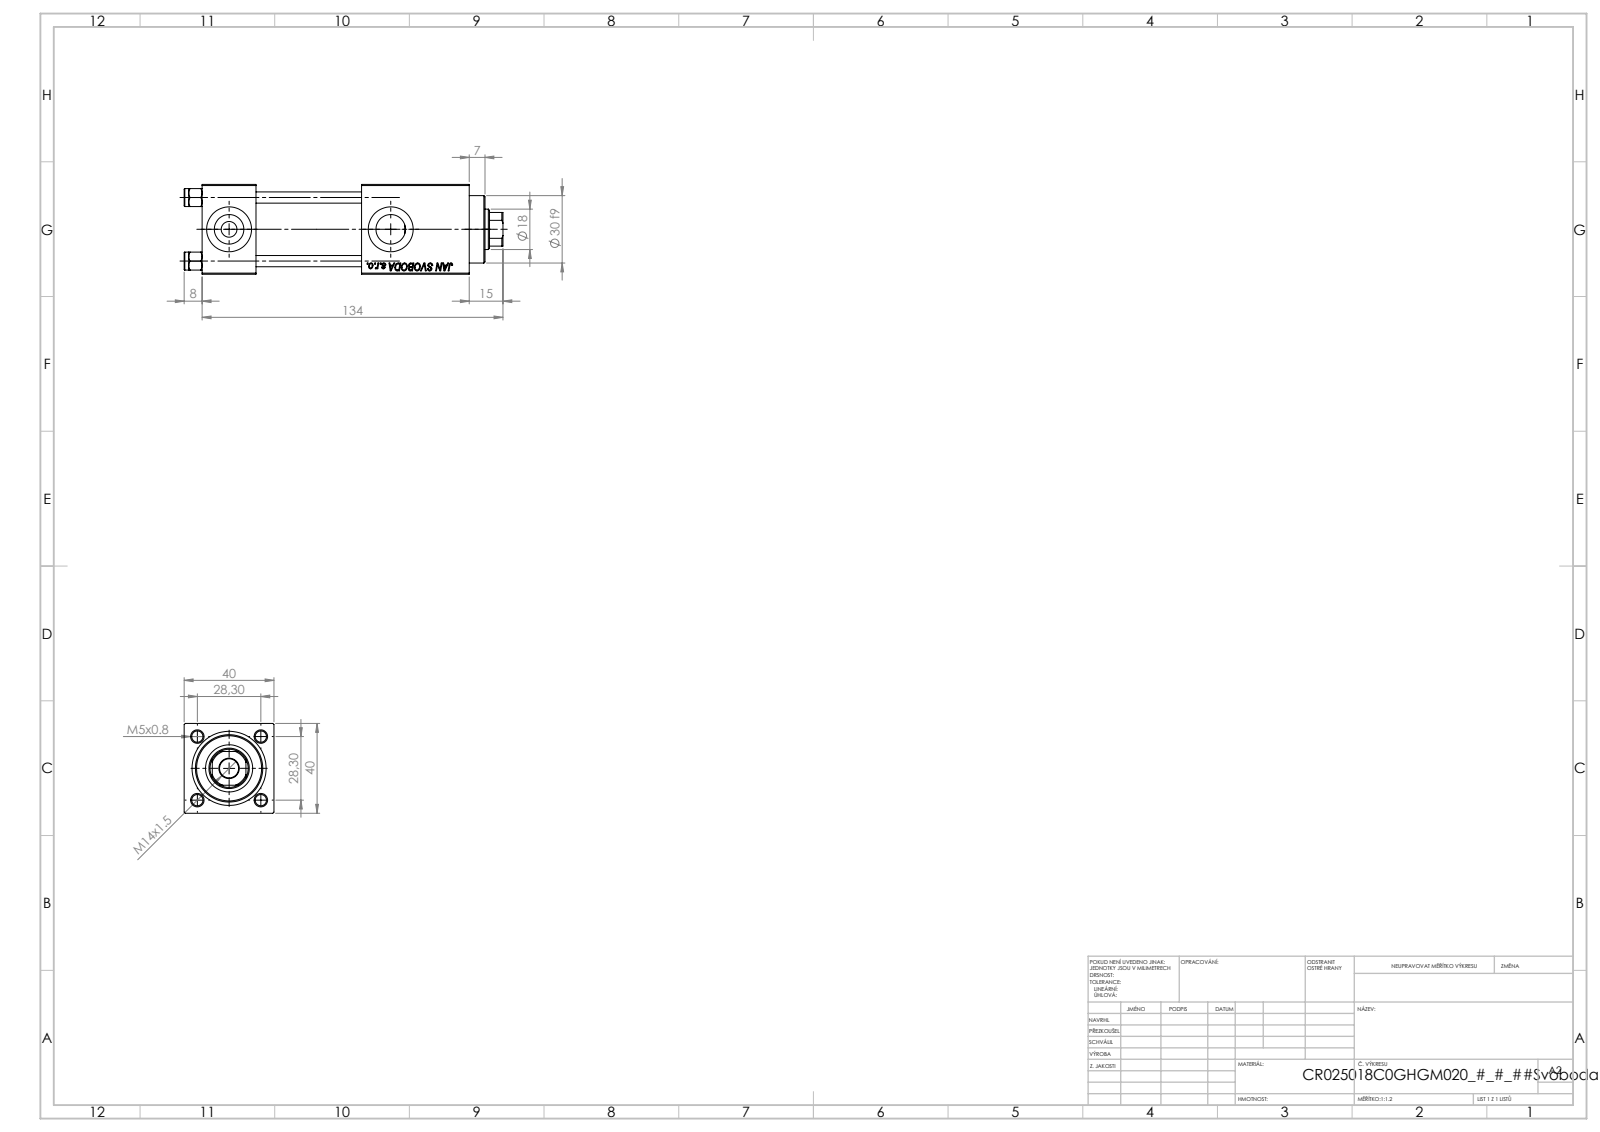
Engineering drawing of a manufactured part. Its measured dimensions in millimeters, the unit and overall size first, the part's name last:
Units: millimetres
Overall size (bounding box): 142 × 40 × 40
Round holes (diameter × count): ⌀5 ×4, ⌀20 ×3, ⌀7 ×2, ⌀13.16 ×2, ⌀8.5 ×1, ⌀18 ×1, ⌀21 ×1, ⌀25 ×1, ⌀30 ×1
Round bosses / shafts (diameter × count): ⌀8 ×4, ⌀31 ×1
Partial cylindrical surfaces — rounded edges, fillets, slot ends (radius × count): R8.5 ×1
Main face-to-face distances: 40, 24, 71, 47, 90.3, 66.3, 19.3, 48, 119, 95
Hole centre spacings: 20.01, 28.3, 40.02, 72
Volume: 149 996 mm³ · Surface area: 56 717 mm²
Bodies: 11 solids, 1144 faces (524 planar, 84 cylindrical, 536 other)
Part name (STEP PRODUCT): V215_VC_A; V215CR_VCP_C; V215CR_C_Body; NUT_M5_C (+1 more)
STEP written by: SolidWorks 2019 (CONFIG_CONTROL_DESIGN)
